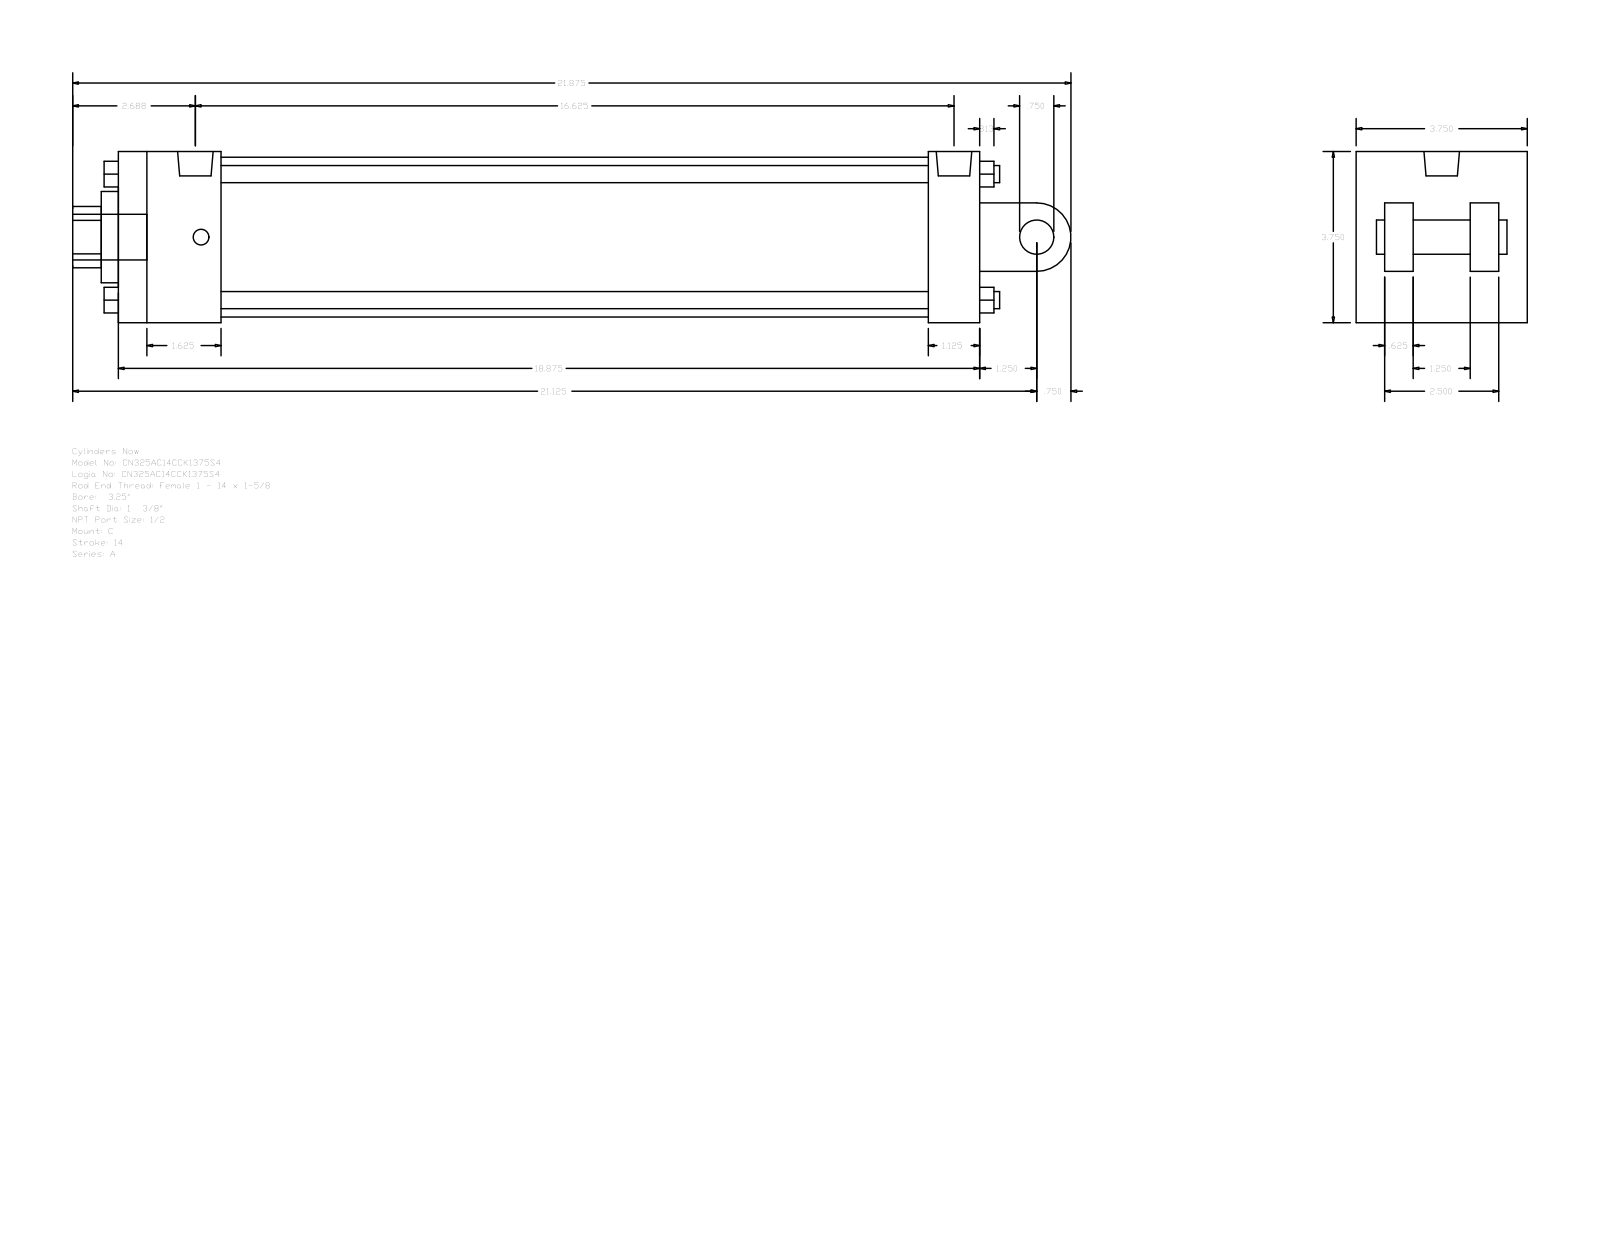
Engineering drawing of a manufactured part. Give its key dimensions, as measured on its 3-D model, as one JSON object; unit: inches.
{"part_name": "A_C__0325_1.375", "step_written_by": "GSSL Pune (CONFIG_CONTROL_DESIGN)", "units": "inches", "bodies": {"solids": 0, "faces": 135, "planar": 102, "cylindrical": 33, "other": 0}, "overall_size": [21.875, 3.75, 3.75], "round_holes": [[0.344, 2], [0.778, 1], [1.375, 1], [2, 1], [3.5, 1]], "round_bosses_or_shafts": [[0.375, 4], [0.344, 2], [1, 1], [0.778, 1], [0.75, 1]], "partial_cylinders_radius": [[0.672, 1], [0.75, 1]], "face_to_face_distances": [3.75, 0.625, 18.875, 1.125, 2.5, 2.625, 1.25, 3.125, 1.875, 17.75], "hole_center_spacings": [0.125]}
